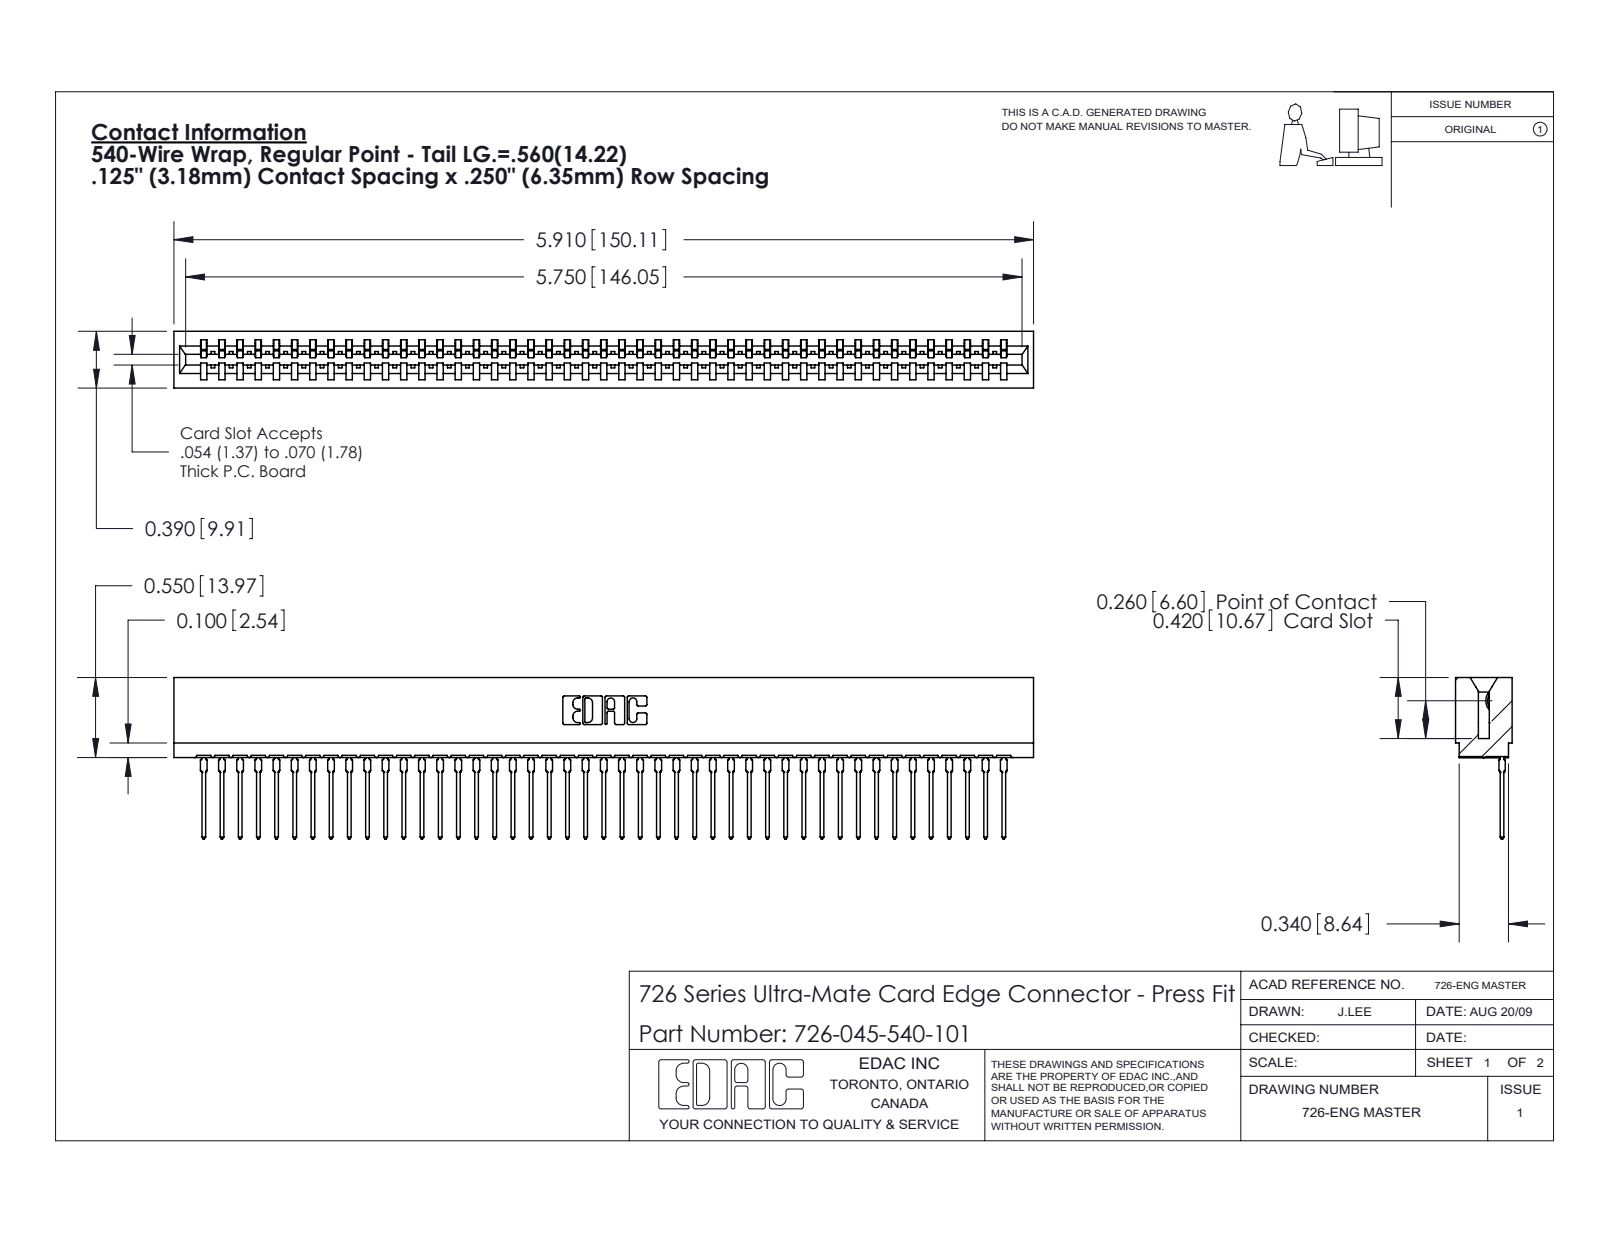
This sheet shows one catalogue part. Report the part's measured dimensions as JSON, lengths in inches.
{"part_name": "726 Part_.515 Slot Depth - 01; 746-292-001_540; 726-045-540-101", "step_written_by": "SolidWorks 2020 (CONFIG_CONTROL_DESIGN)", "units": "inches", "bodies": {"solids": 46, "faces": 4957, "planar": 2890, "cylindrical": 897, "other": 1170}, "overall_size": [5.91, 1.109, 0.39], "volume_in3": 0.824, "surface_area_in2": 32.82, "partial_cylinders_radius": [[0.021, 90], [0.015, 46], [0.01, 22], [0.007, 6], [0.031, 6], [0.005, 4], [0.011, 4], [0.026, 3]], "face_to_face_distances": [0.057, 0.333, 0.39, 0.025, 0.307, 0.25, 0.083, 0.275, 0.365, 0.032]}
